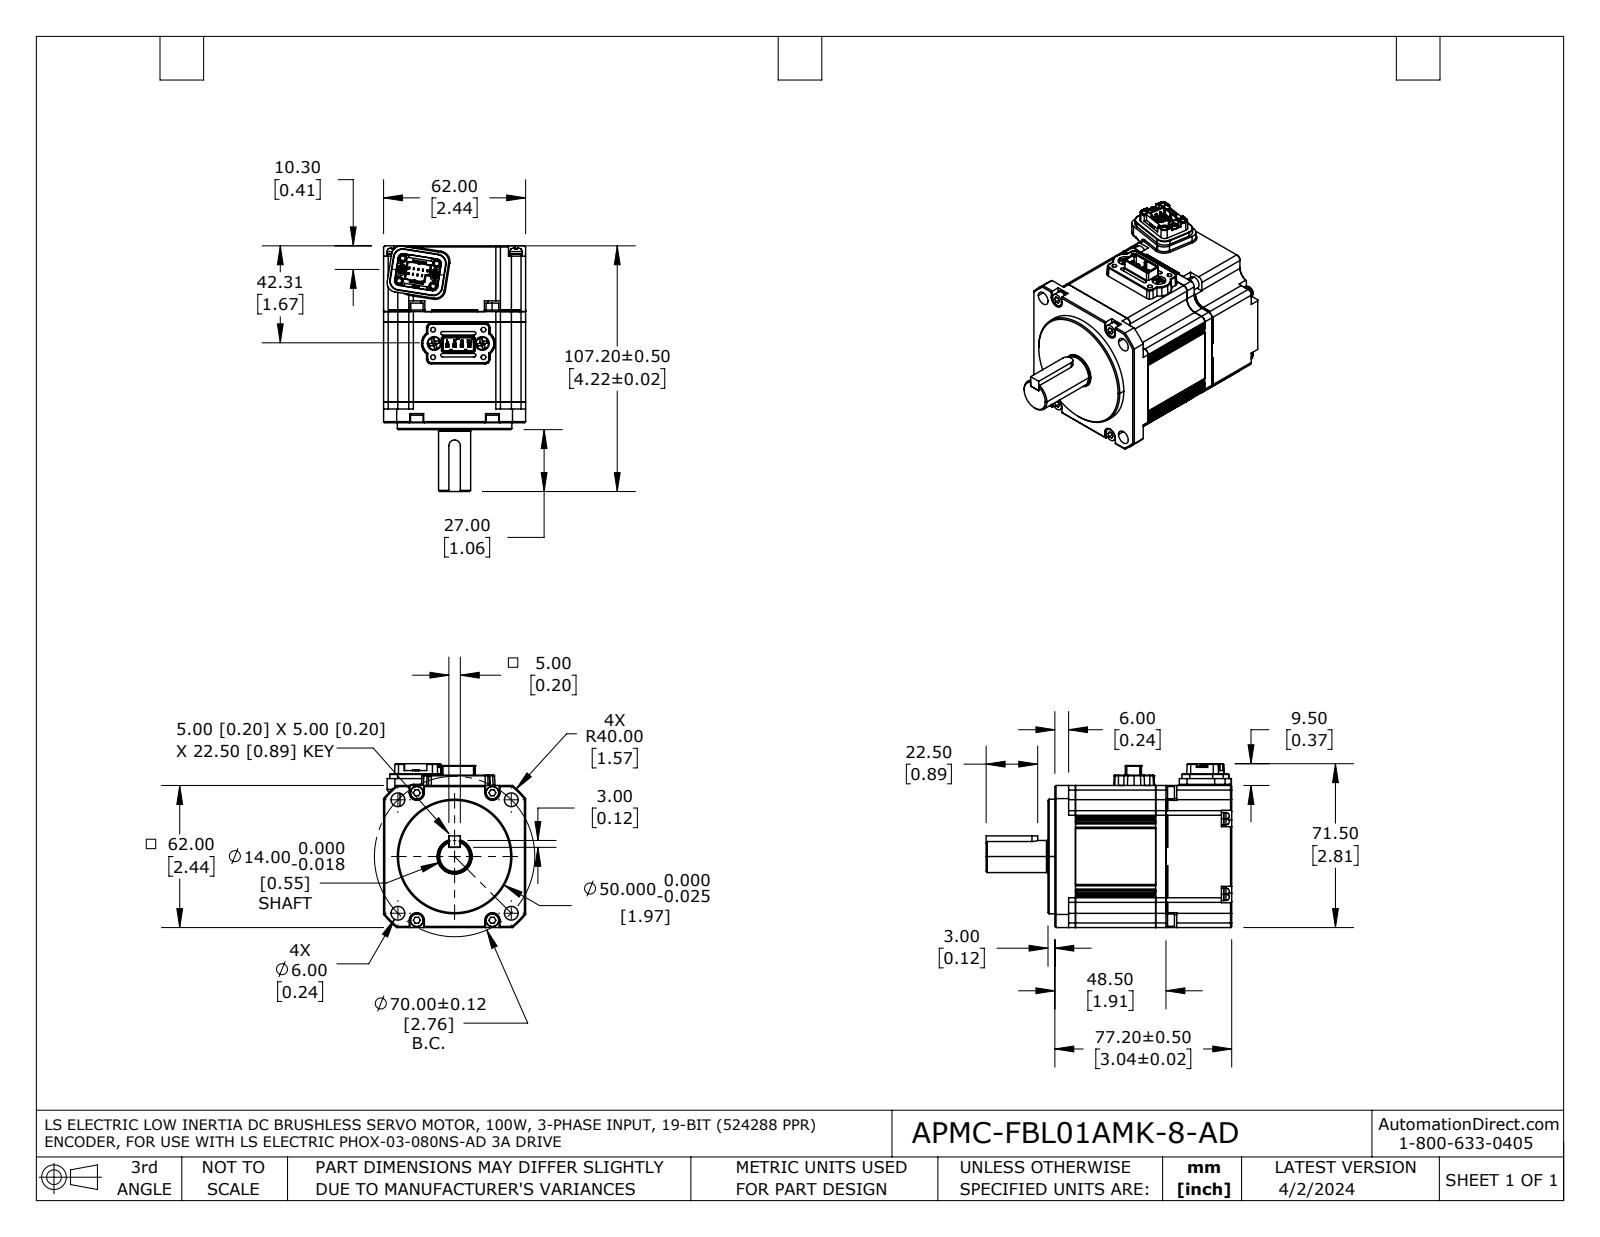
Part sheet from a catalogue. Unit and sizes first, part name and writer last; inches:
Units: inches
Overall size (bounding box): 4.22 × 2.815 × 2.441
Round holes (diameter × count): ⌀0.083 ×10, ⌀0.138 ×8, ⌀0.118 ×6, ⌀0.236 ×6, ⌀0.122 ×4, ⌀0.079 ×2, ⌀0.13 ×1, ⌀0.134 ×1, ⌀0.602 ×1
Round bosses / shafts (diameter × count): ⌀0.213 ×6, ⌀0.22 ×4, ⌀0.217 ×4, ⌀0.118 ×4, ⌀0.087 ×2, ⌀1.969 ×1, ⌀0.591 ×1, ⌀0.583 ×1
Partial cylindrical surfaces — rounded edges, fillets, slot ends (radius × count): R0.008 ×20, R0.012 ×20, R0.039 ×12, R0.006 ×9, R0.079 ×8, R0.118 ×8, R0.018 ×7, R0.004 ×6
Main face-to-face distances: 0.177, 1.378, 0.028, 1.555, 0.205, 1.583, 2.441, 0.118, 1.13, 1.102
Hole centre spacings: 1.762, 0.237, 0.335, 0.346, 0.602, 0.63, 0.879, 1.239
Volume: 16.83 in³ · Surface area: 106 in²
Bodies: 45 solids, 1909 faces (1167 planar, 543 cylindrical, 199 other)
Part name (STEP PRODUCT): APMC-FBL01AMK-8-AD
STEP written by: SolidWorks 2021 (AUTOMOTIVE_DESIGN)
